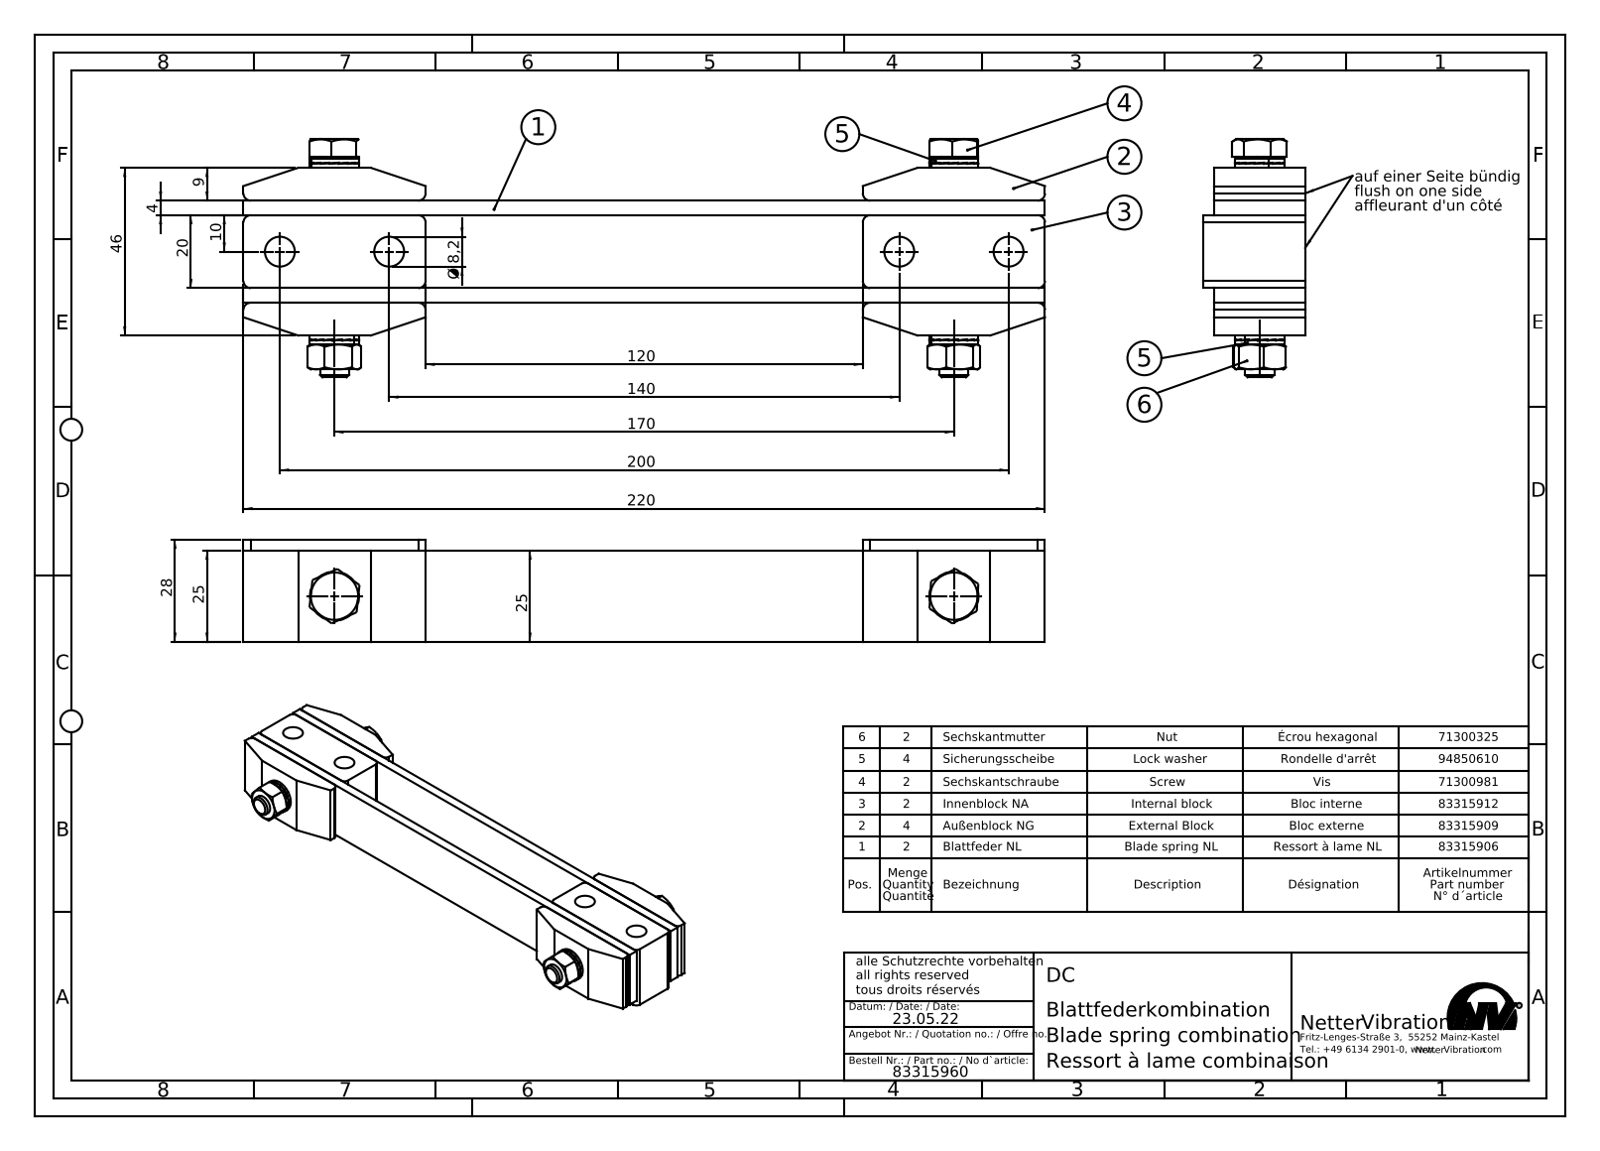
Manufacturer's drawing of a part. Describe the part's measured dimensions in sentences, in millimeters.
The part is named "Blattfederkombination DC # 83315960". Its 3-D file was written by "SolidWorks 2015 (AUTOMOTIVE_DESIGN)". It is 16 solids with 694 faces: 558 planar, 84 cylindrical and 52 other. Overall it measures 220 by 65.3 by 28 millimeters. Its volume is 136 158 cubic millimeters and its surface area 61 956 square millimeters. Round holes: 6 of diameter 8.2, 2 of diameter 6.8, 2 of diameter 8, 2 of diameter 8.5, 2 of diameter 8.7. Round bosses or shafts: 2 of diameter 13.5, 2 of diameter 13. Partial cylindrical surfaces (rounded edges, fillets, slot ends): 16 of radius 2. The main face-to-face distances are 4, 24, 28, 20, 25, 13, 9, 33, 37, 3. The hole center spacings are 170, 30, 140, 200.
